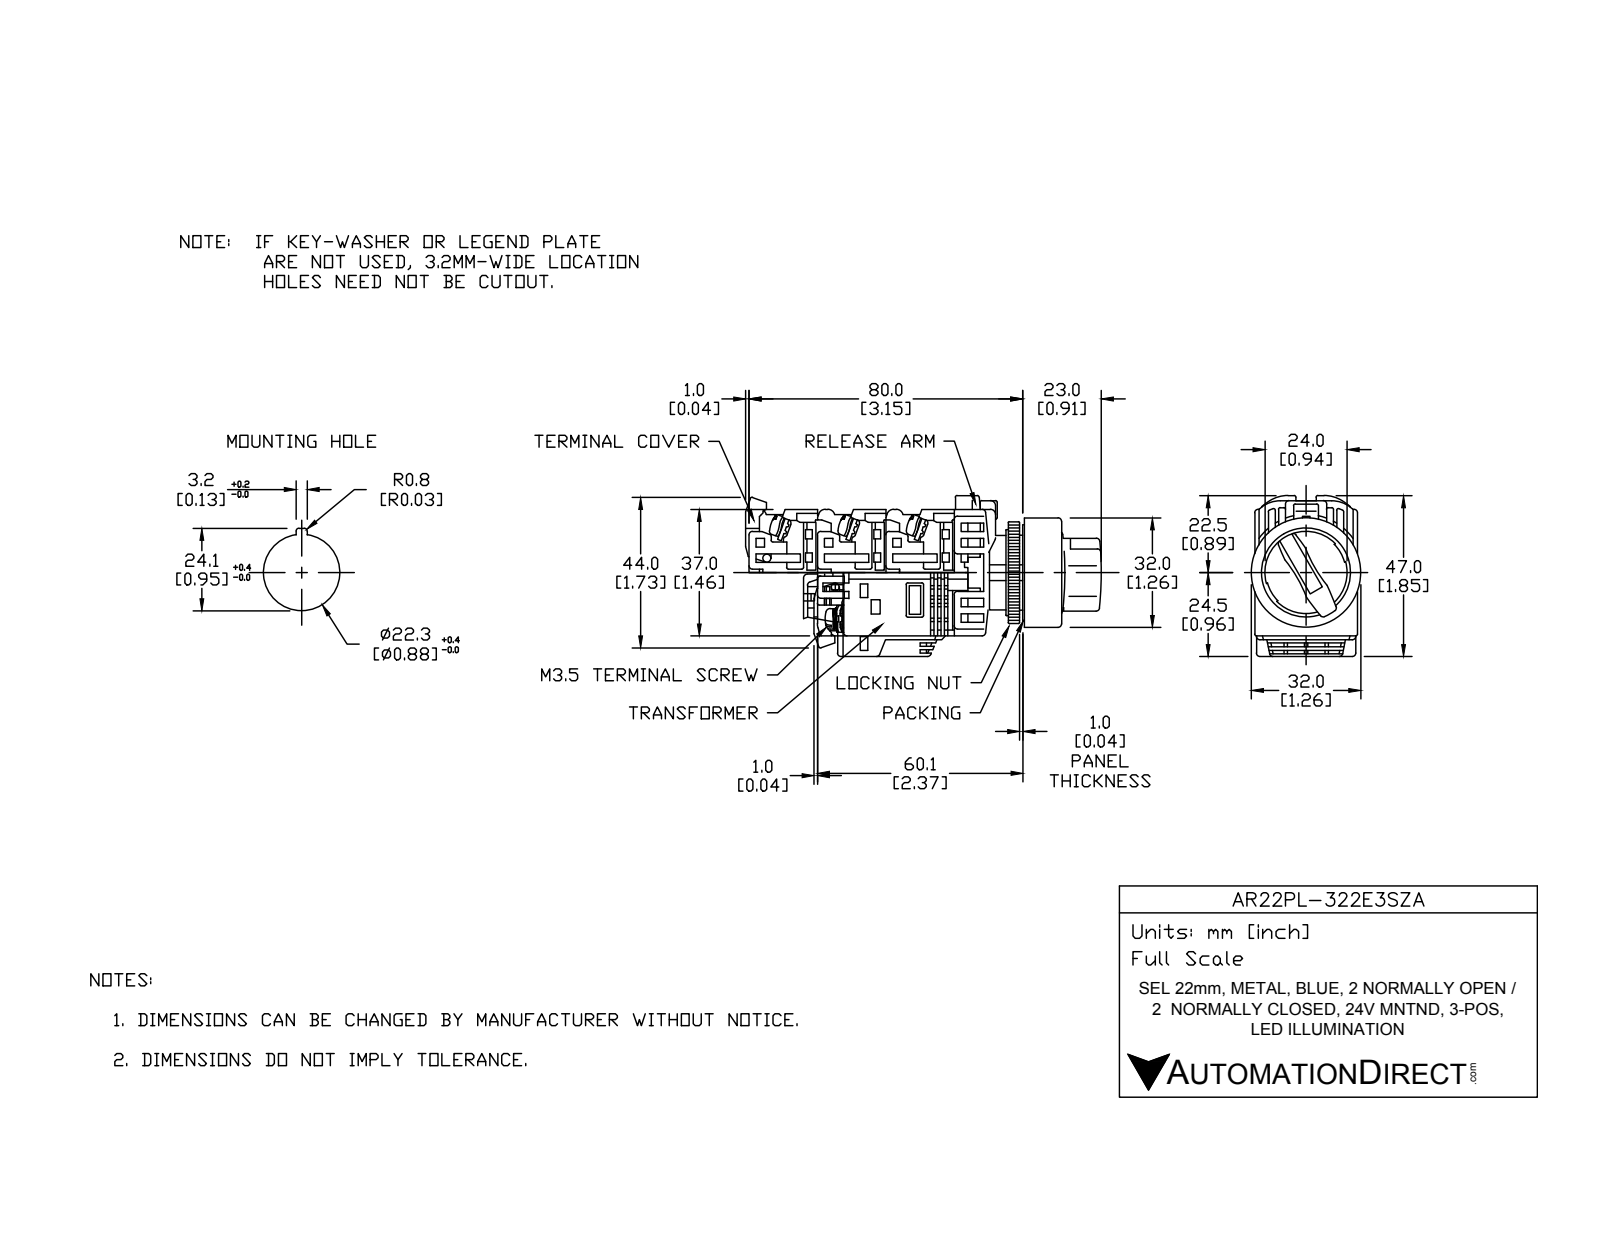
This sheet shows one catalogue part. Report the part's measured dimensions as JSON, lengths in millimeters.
{"part_name": "AR22PL-322E3SZA", "step_written_by": "SolidWorks 2017 (AUTOMOTIVE_DESIGN)", "units": "millimeters", "bodies": {"solids": 33, "faces": 744, "planar": 524, "cylindrical": 181, "other": 39}, "overall_size": [104.5, 43.81, 32], "volume_mm3": 64125, "surface_area_mm2": 35355, "round_holes": [[21.8, 1], [22, 1], [25, 1], [31, 1]], "round_bosses_or_shafts": [[5, 10], [32, 1], [30.5, 1], [29.8, 1], [24, 1], [21.75, 1], [17, 1]], "partial_cylinders_radius": [[0.5, 66], [1.75, 8], [1, 6], [5, 4], [4, 2], [12, 1], [16.59, 1], [17.59, 1]], "face_to_face_distances": [20, 1, 18, 40, 29, 3, 9, 10, 2, 19]}
